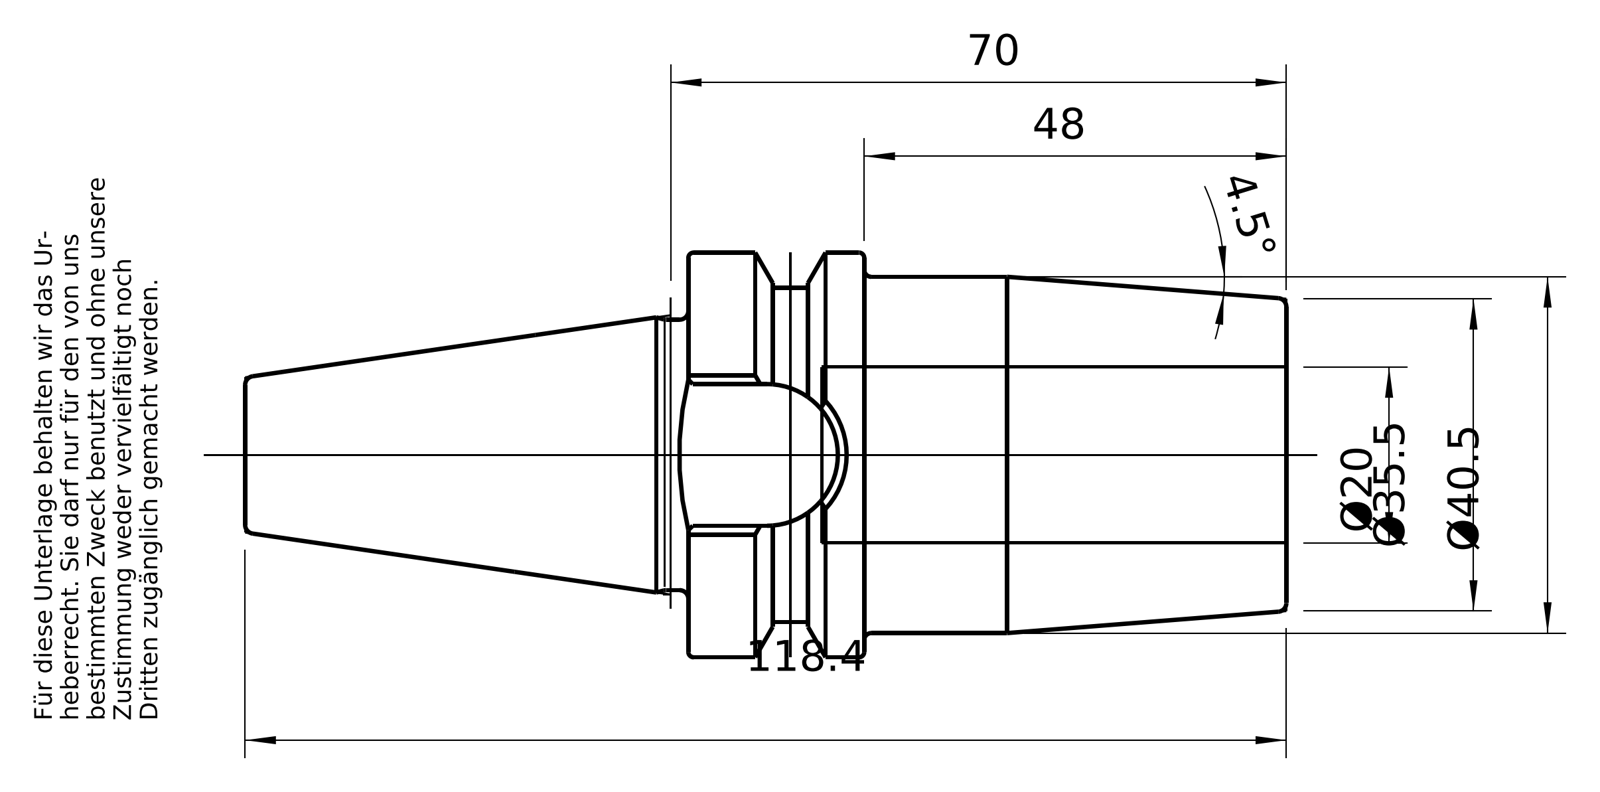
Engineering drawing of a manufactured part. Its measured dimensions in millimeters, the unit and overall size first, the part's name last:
Units: millimetres
Overall size (bounding box): 118.4 × 45.98 × 45.98
Round holes (diameter × count): ⌀10.11 ×1, ⌀12.51 ×1, ⌀13 ×1, ⌀20 ×1
Round bosses / shafts (diameter × count): ⌀45.98 ×1, ⌀40.5 ×1, ⌀30.75 ×1, ⌀12.01 ×1
Partial cylindrical surfaces — rounded edges, fillets, slot ends (radius × count): R8.1 ×1, R18.88 ×1
Main face-to-face distances: 68, 16, 52, 32.3, 20, 4, 48, 16.2, 50.4, 66.4
Volume: 90 175 mm³ · Surface area: 20 599 mm²
Bodies: 1 solid, 96 faces (26 planar, 22 cylindrical, 48 other)
Part name (STEP PRODUCT): 30-645-20
STEP written by: PRO/ENGINEER BY PARAMETRIC TECHNOLOGY CORPORATION, 2010430 (CONFIG_CONTROL_DESIGN)
